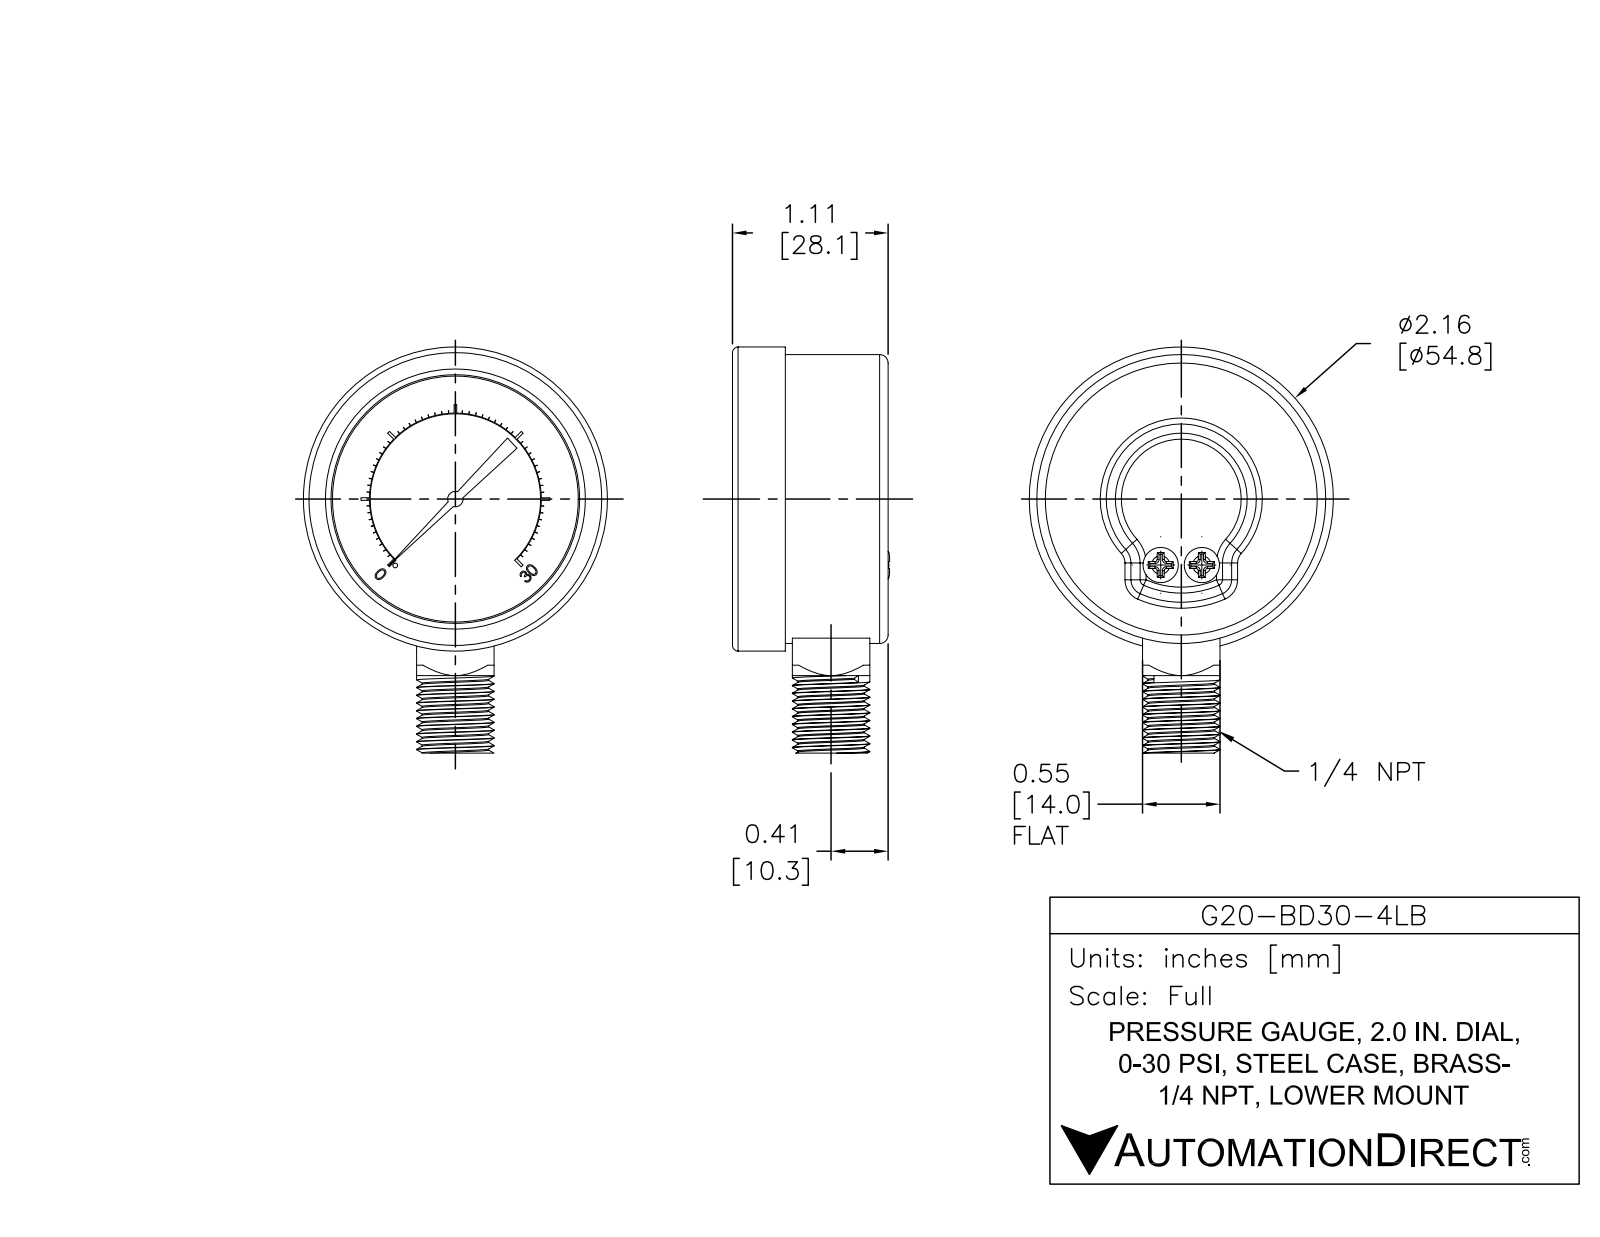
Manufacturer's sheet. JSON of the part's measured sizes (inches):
{"part_name": "G20-BD30-4LB", "step_written_by": "SolidWorks 2021 (AUTOMOTIVE_DESIGN)", "units": "inches", "bodies": {"solids": 1, "faces": 420, "planar": 269, "cylindrical": 81, "other": 70}, "overall_size": [2.882, 2.158, 1.115], "volume_in3": 3.182, "surface_area_in2": 18.02, "round_holes": [[0.14, 1], [1.745, 1]], "round_bosses_or_shafts": [[0.25, 2], [2.158, 1], [2.05, 1], [0.55, 1], [0.11, 1], [0.033, 1]], "partial_cylinders_radius": [[0.06, 4], [0.605, 1], [0.61, 1]], "face_to_face_distances": [0.815, 1.105, 0.29, 0.1, 0.715, 1.005, 0.63, 0.73, 0.085, 0.375]}
